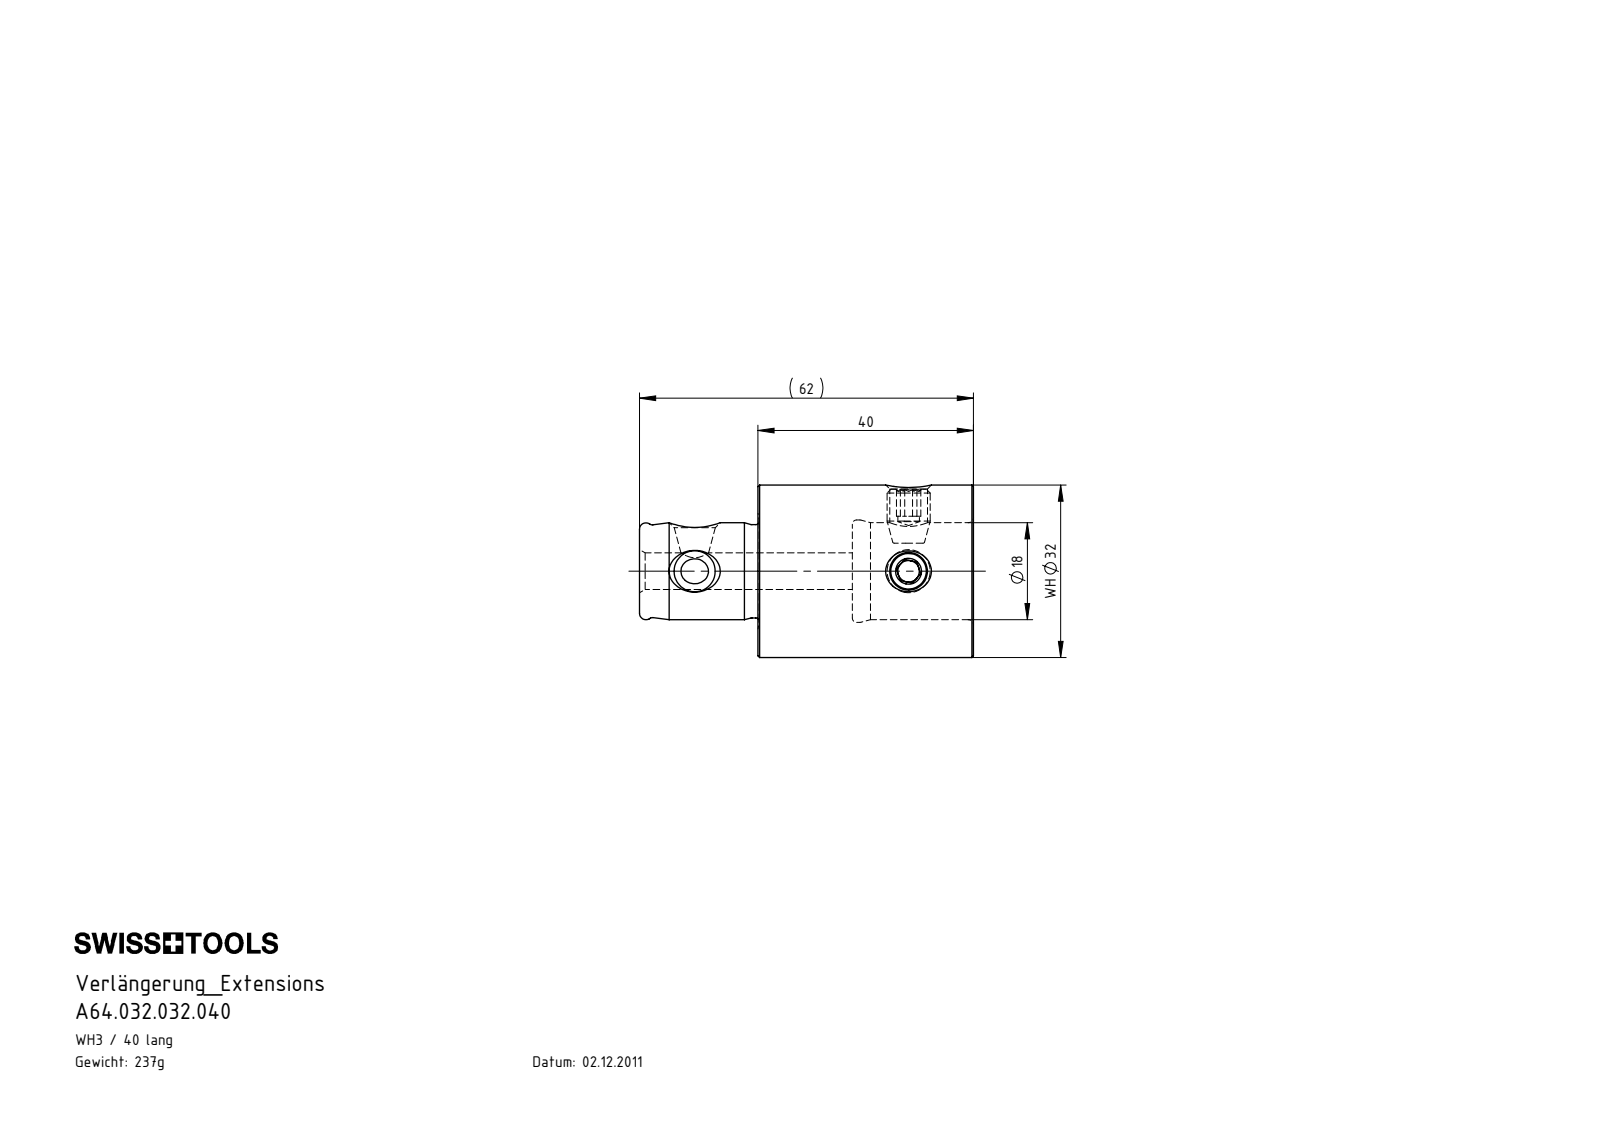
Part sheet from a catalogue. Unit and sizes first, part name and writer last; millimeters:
Units: millimetres
Overall size (bounding box): 62 × 32 × 32
Round holes (diameter × count): ⌀7 ×2, ⌀6.8 ×1, ⌀18 ×1, ⌀19 ×1
Round bosses / shafts (diameter × count): ⌀8 ×2, ⌀32 ×1, ⌀17.3 ×1
Main face-to-face distances: 40, 17.5, 22.5, 22, 39.5, 62, 5, 4, 10, 3.99
Volume: 30 224 mm³ · Surface area: 9 841 mm²
Bodies: 3 solids, 94 faces (22 planar, 20 cylindrical, 52 other)
Part name (STEP PRODUCT): WH3-ER1.001.010; WH3-WH3.001.040_A; WH3-WH3.001.040
STEP written by: SolidWorks 2015 (AUTOMOTIVE_DESIGN)
